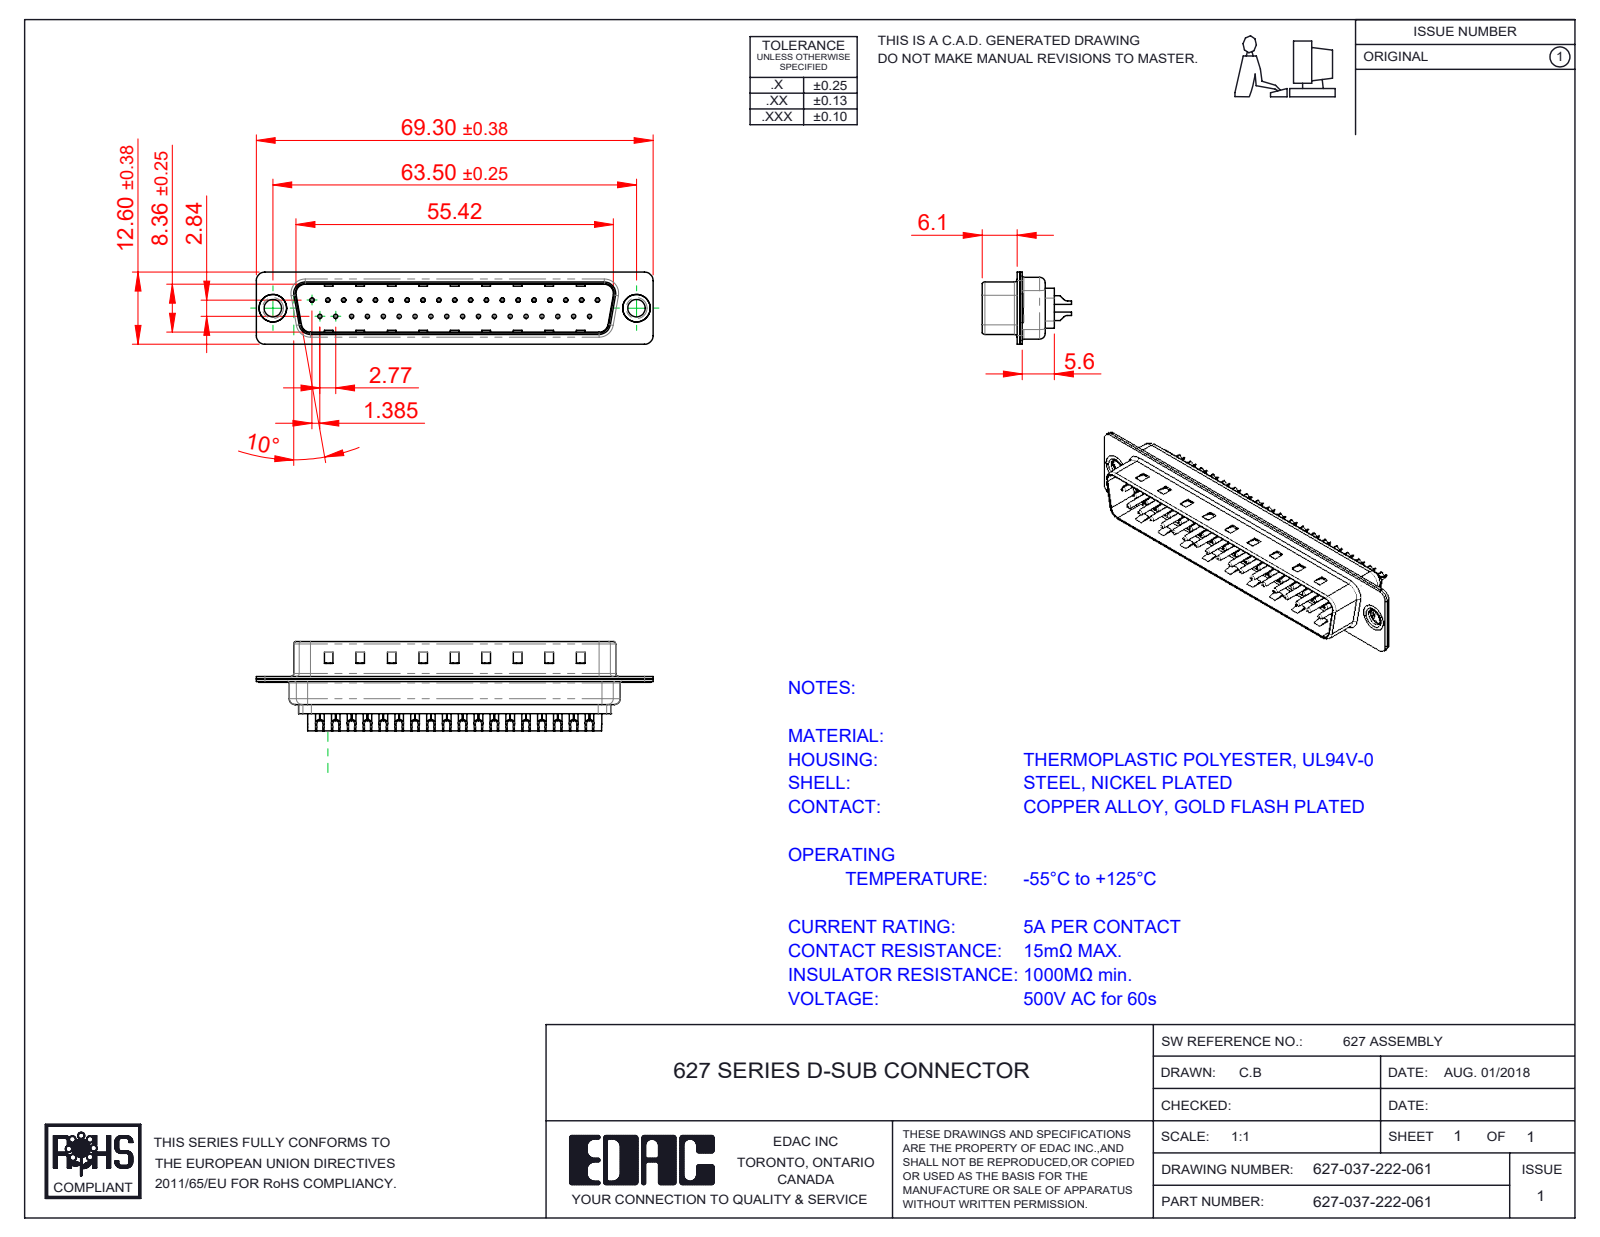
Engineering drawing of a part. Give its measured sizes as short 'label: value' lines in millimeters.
name: 627-037-222-061; 627 Thru Hole Rivet; 627 Contact Row 2_22L; 627 Shell Front_37 Contacts (+3 more)
written by: SolidWorks 2020 (CONFIG_CONTROL_DESIGN)
unit: mm
bodies: 42 solids, 2754 faces (721 planar, 1198 cylindrical, 835 other)
size: 69.3 × 15.35 × 12.6
volume: 3 636 mm³; area: 10 612 mm²
holes: 37× ⌀0.35, 37× ⌀1.1, 37× ⌀1.6, 2× ⌀3.05, 2× ⌀4, 2× ⌀4.8
bosses: 37× ⌀2, 37× ⌀1.5, 37× ⌀0.75, 2× ⌀5, 2× ⌀4.9, 2× ⌀3.55
rounds: 16× R1.5, 12× R2, 8× R0.5, 8× R1.6, 6× R1, 4× R0.25, 4× R0.6, 4× R0.65
face distances: 0.4, 0.82, 9.58, 0.45, 8.76, 0.9, 1.5, 1.4, 6.05, 0.5
hole spacings: 3.16, 2.77, 5.54, 8.31, 5.04, 10.1, 11.08, 12.78
